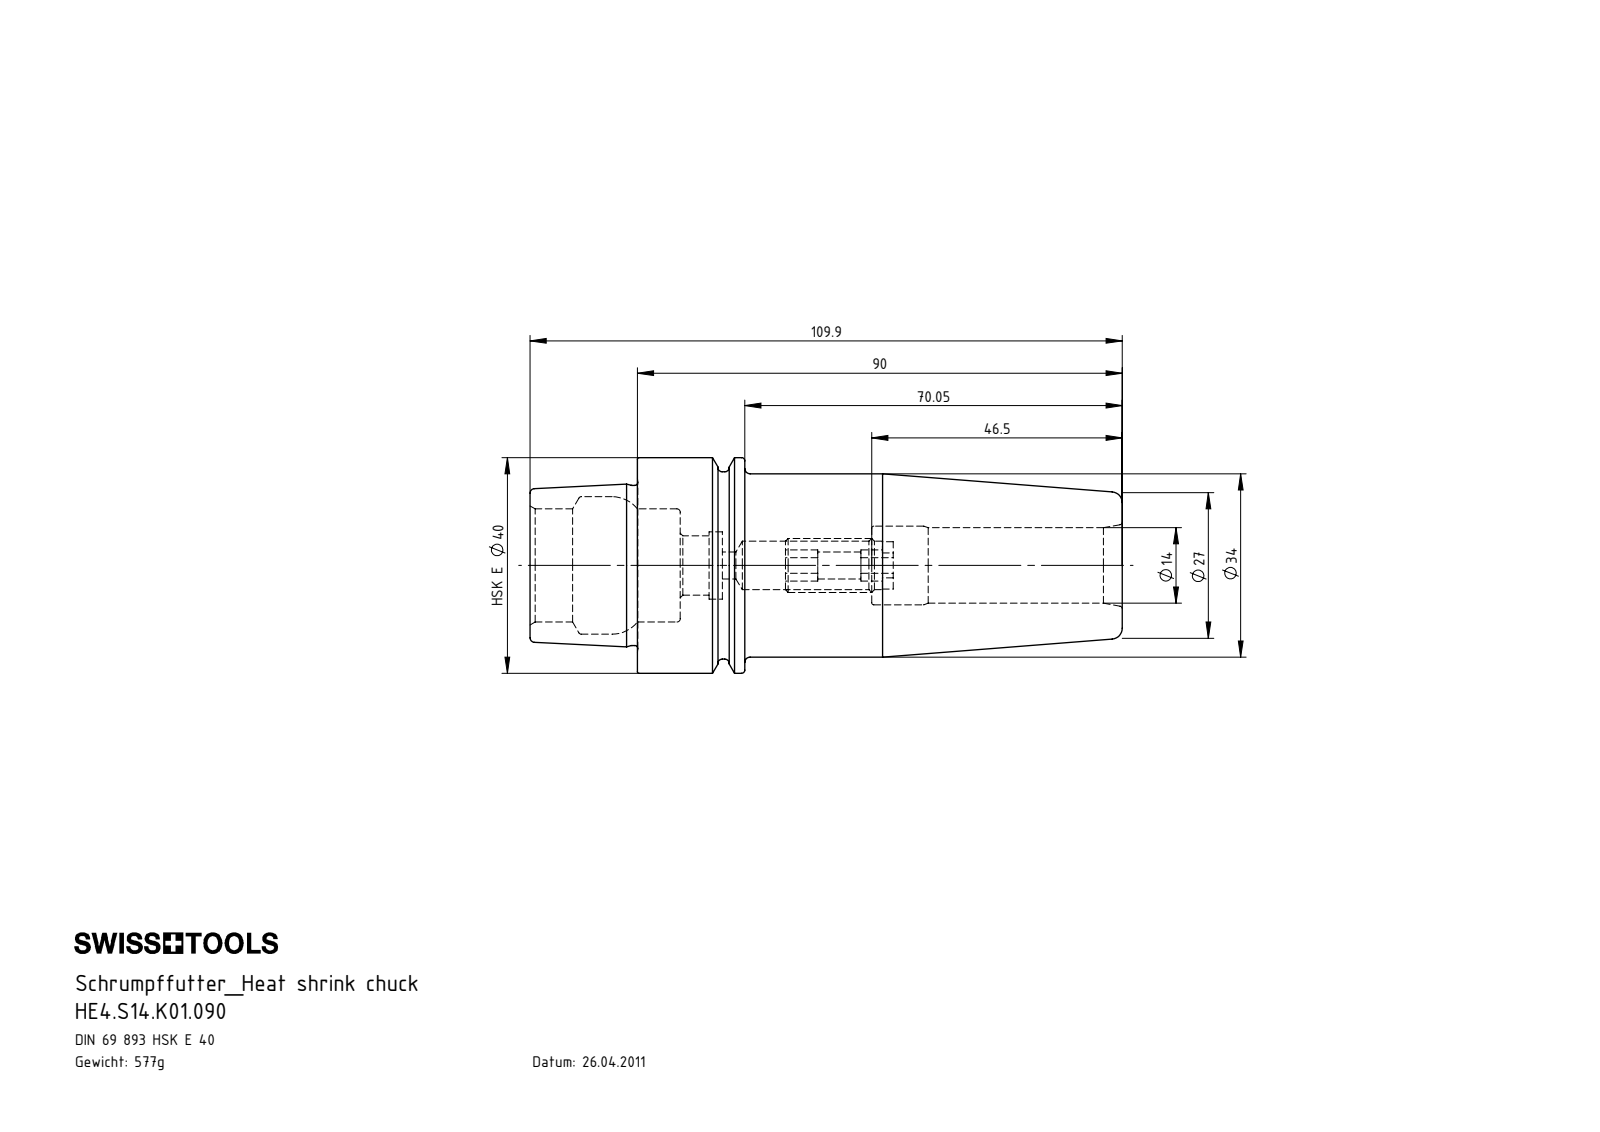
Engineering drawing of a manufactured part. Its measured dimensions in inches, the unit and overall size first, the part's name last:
Units: inches
Overall size (bounding box): 4.327 × 1.575 × 1.575
Round holes (diameter × count): ⌀0.197 ×1, ⌀0.354 ×1, ⌀0.433 ×1, ⌀0.492 ×1, ⌀0.551 ×1, ⌀0.575 ×1, ⌀0.827 ×1, ⌀1.004 ×1
Round bosses / shafts (diameter × count): ⌀1.575 ×1, ⌀1.368 ×1, ⌀1.339 ×1, ⌀1.17 ×1, ⌀0.394 ×1
Main face-to-face distances: 3.543, 0.313, 3.23, 0.783, 1.096, 4.327, 0.472, 1.569, 0.785, 2.758
Volume: 4.488 in³ · Surface area: 30.65 in²
Bodies: 2 solids, 137 faces (43 planar, 34 cylindrical, 60 other)
Part name (STEP PRODUCT): HE4.S14.K01.090; ERU-AN4.K01.020_A; HE4-S14.K01.090_B_Fertigbearbeitung
STEP written by: SolidWorks 2012 (AUTOMOTIVE_DESIGN)
